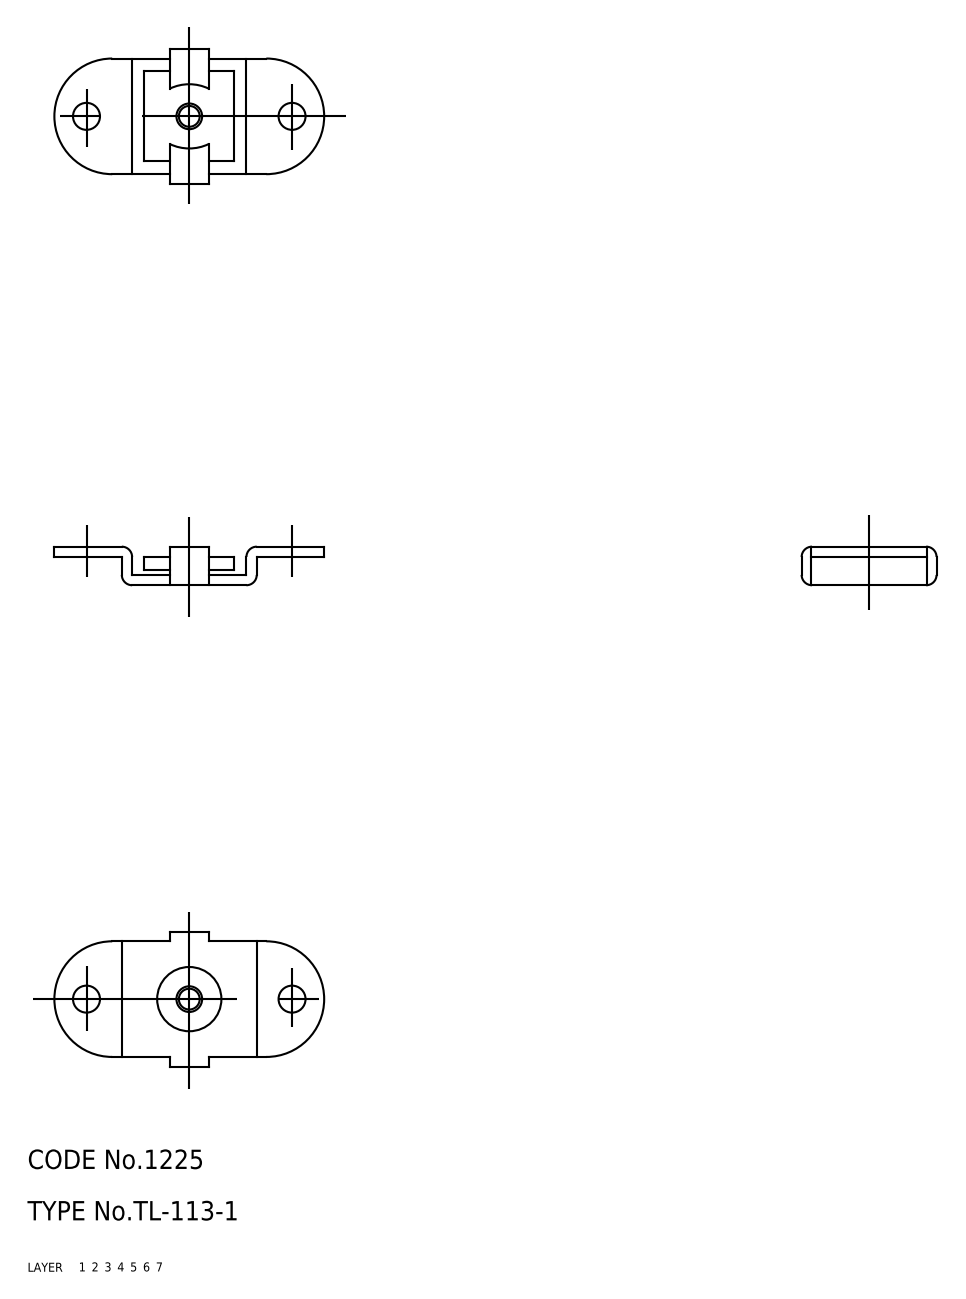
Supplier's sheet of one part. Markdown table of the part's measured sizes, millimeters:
| quantity | value |
| --- | --- |
| part name | 67111453; 67111466 |
| STEP written by | CADfix (AUTOMOTIVE_DESIGN) |
| units | millimeters |
| bodies | 2 solids, 52 faces (0 planar, 0 cylindrical, 52 other) |
| overall size | 42 × 21 × 6 |
| volume | 1 688 mm³ |
| surface area | 2 503 mm² |
